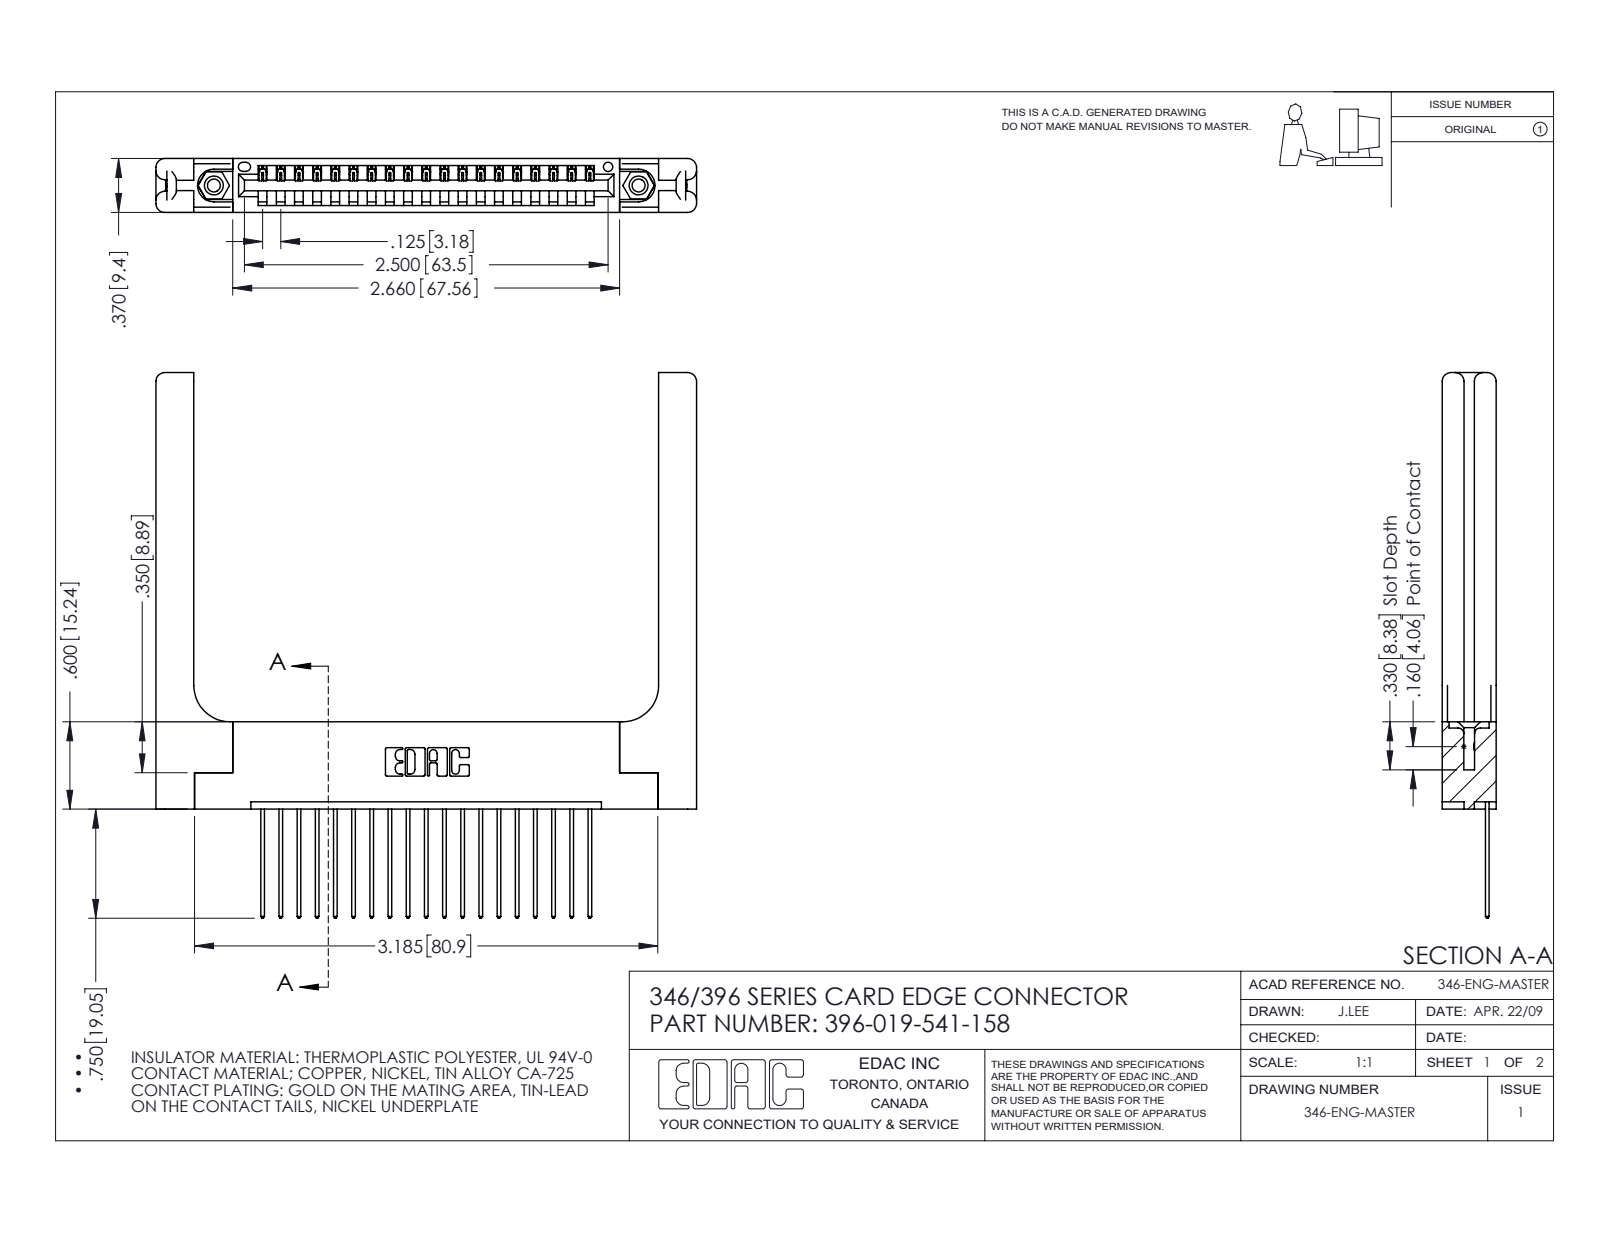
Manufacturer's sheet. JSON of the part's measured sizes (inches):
{"part_name": "345-292-001_345-293-141; 346-220-058_345-220-058; 396-019-541-158; 346 Part_Flush Mounting Lugs - 0.156 Dia-TH (+1 more)", "step_written_by": "SolidWorks 2016 (CONFIG_CONTROL_DESIGN)", "units": "inches", "bodies": {"solids": 24, "faces": 1480, "planar": 984, "cylindrical": 436, "other": 60}, "overall_size": [3.75, 3.716, 0.37], "volume_in3": 1.004, "surface_area_in2": 25.53, "round_holes": [[0.089, 2], [0.125, 2], [0.156, 2], [0.064, 1]], "round_bosses_or_shafts": [[0.155, 2]], "partial_cylinders_radius": [[0.006, 38], [0.01, 38], [0.01, 22], [0.06, 16], [0.007, 6], [0.031, 6], [0.026, 3], [0.03, 2]], "face_to_face_distances": [0.37, 0.072, 0.048, 0.322, 0.15, 0.148, 0.25, 0.298, 0.025, 0.102], "hole_center_spacings": [0.246, 2.713, 2.92]}
